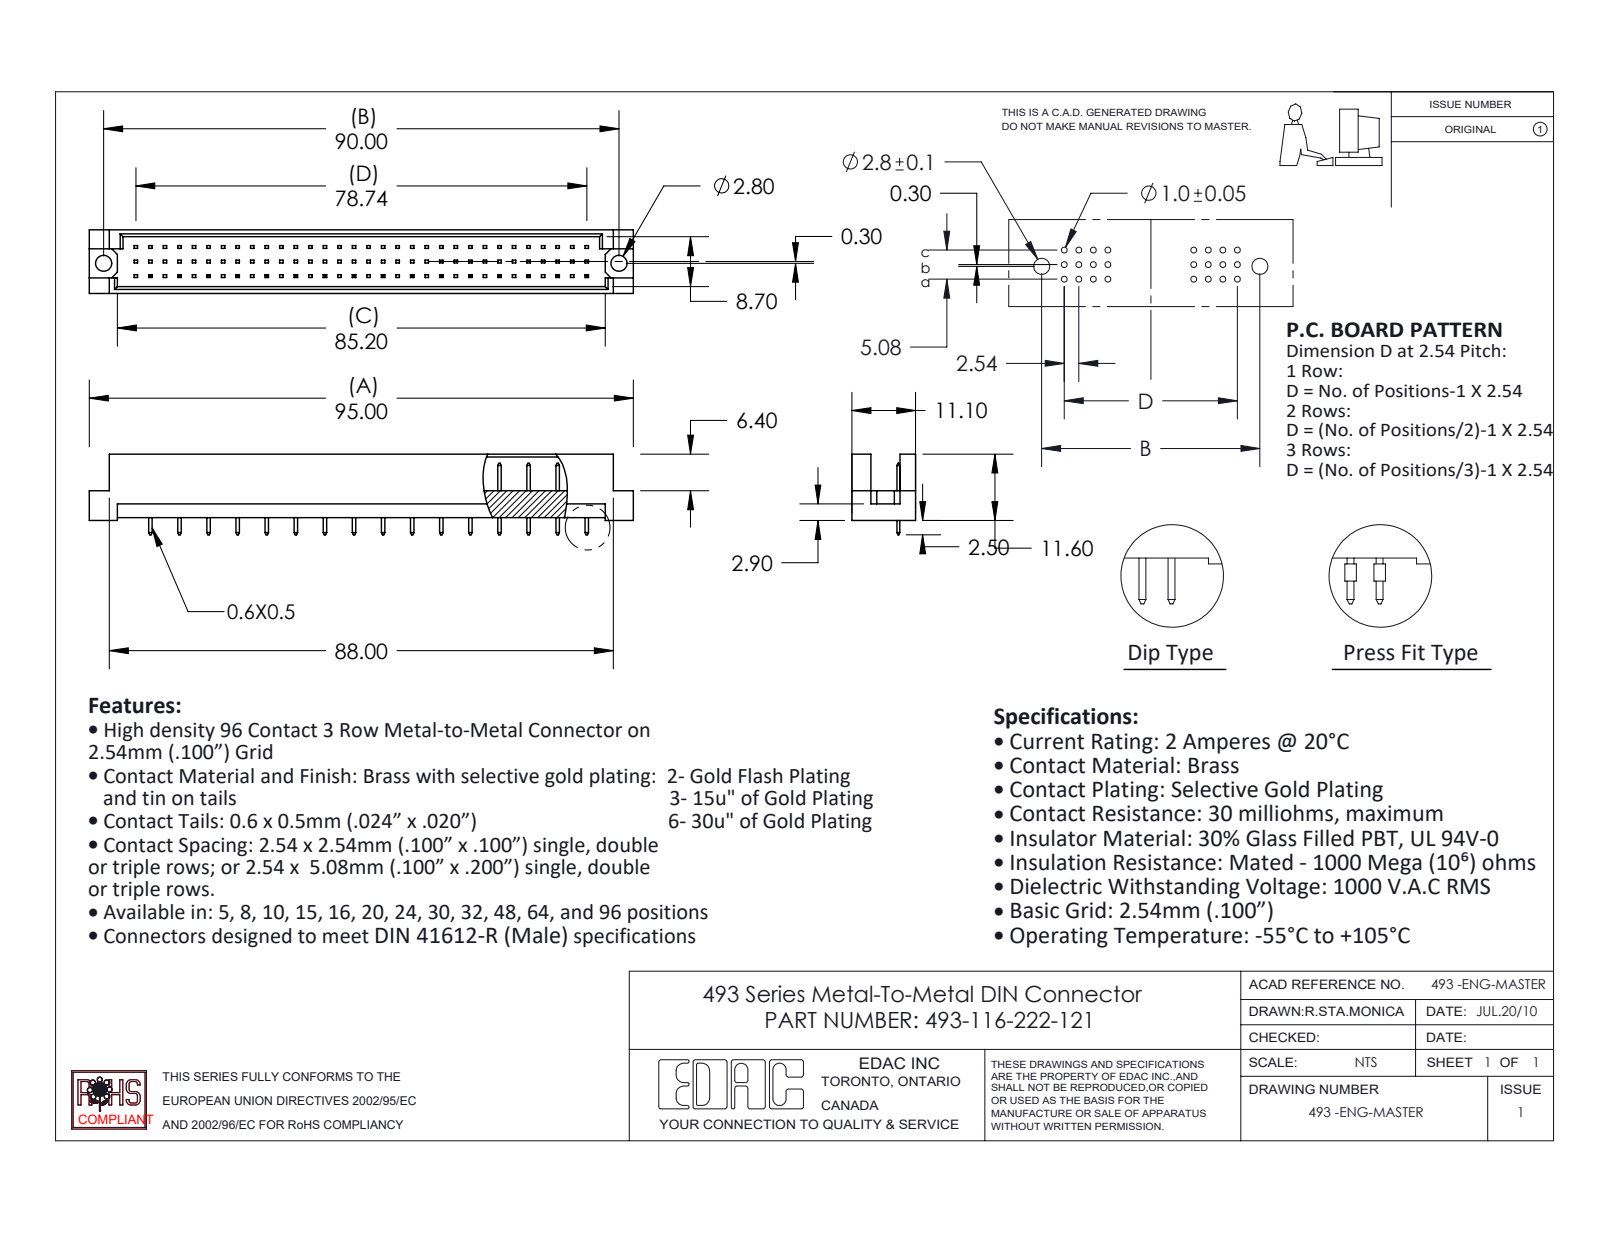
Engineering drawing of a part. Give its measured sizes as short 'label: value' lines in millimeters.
name: 493-116-222-122; 493 Part_96; 493-290_22
written by: SolidWorks 2020 (CONFIG_CONTROL_DESIGN)
unit: mm
bodies: 17 solids, 660 faces (656 planar, 4 cylindrical, 0 other)
size: 95 × 14.1 × 11.1
volume: 5 718 mm³; area: 6 909 mm²
holes: 2× ⌀2.8
face distances: 1.2, 9.9, 11.1, 8.7, 4.7, 0.5, 5.08, 2.54, 2.76, 3.26
hole spacings: 90
